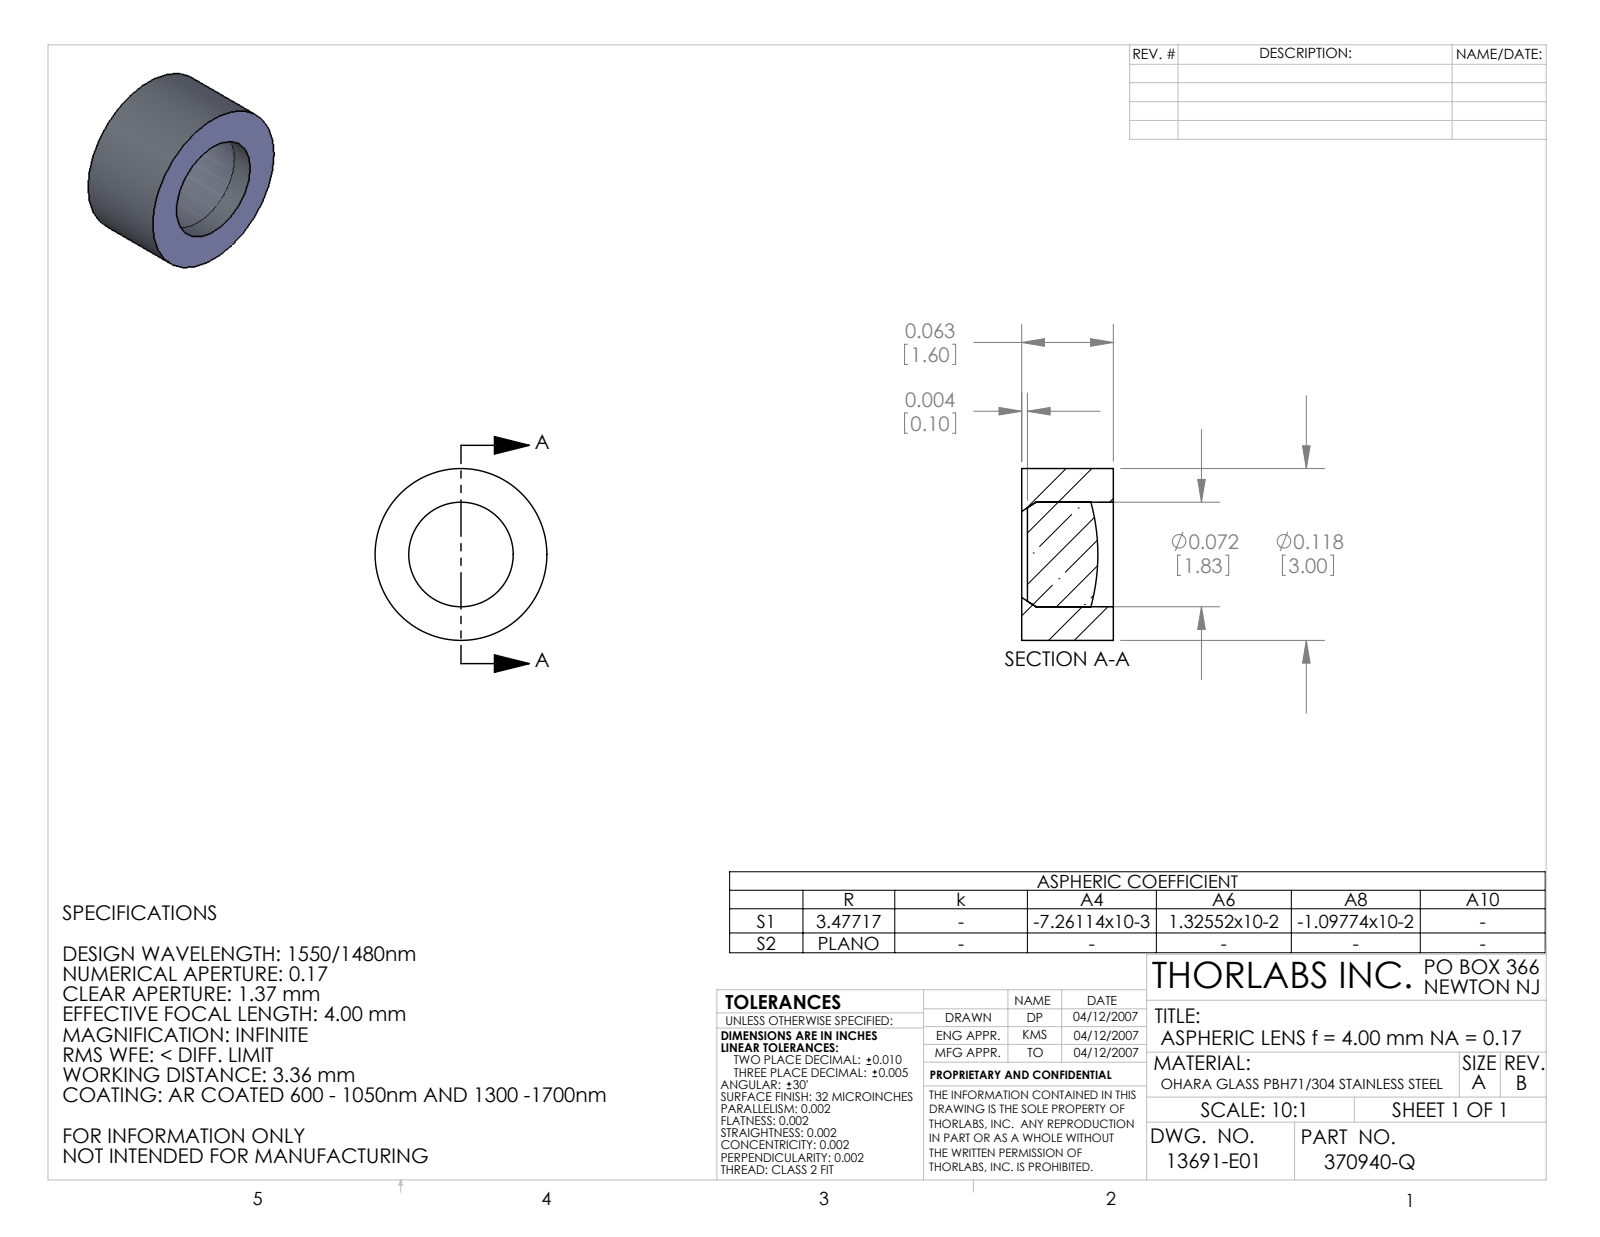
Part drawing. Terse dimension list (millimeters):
name: 13691-E0W
written by: SolidWorks 2007 (AUTOMOTIVE_DESIGN)
unit: mm
bodies: 0 solids, 11 faces (3 planar, 4 cylindrical, 4 other)
size: 3 × 3 × 1.6
holes: 1× ⌀1.8
bosses: 1× ⌀3
face distances: 1.6, 1.5
